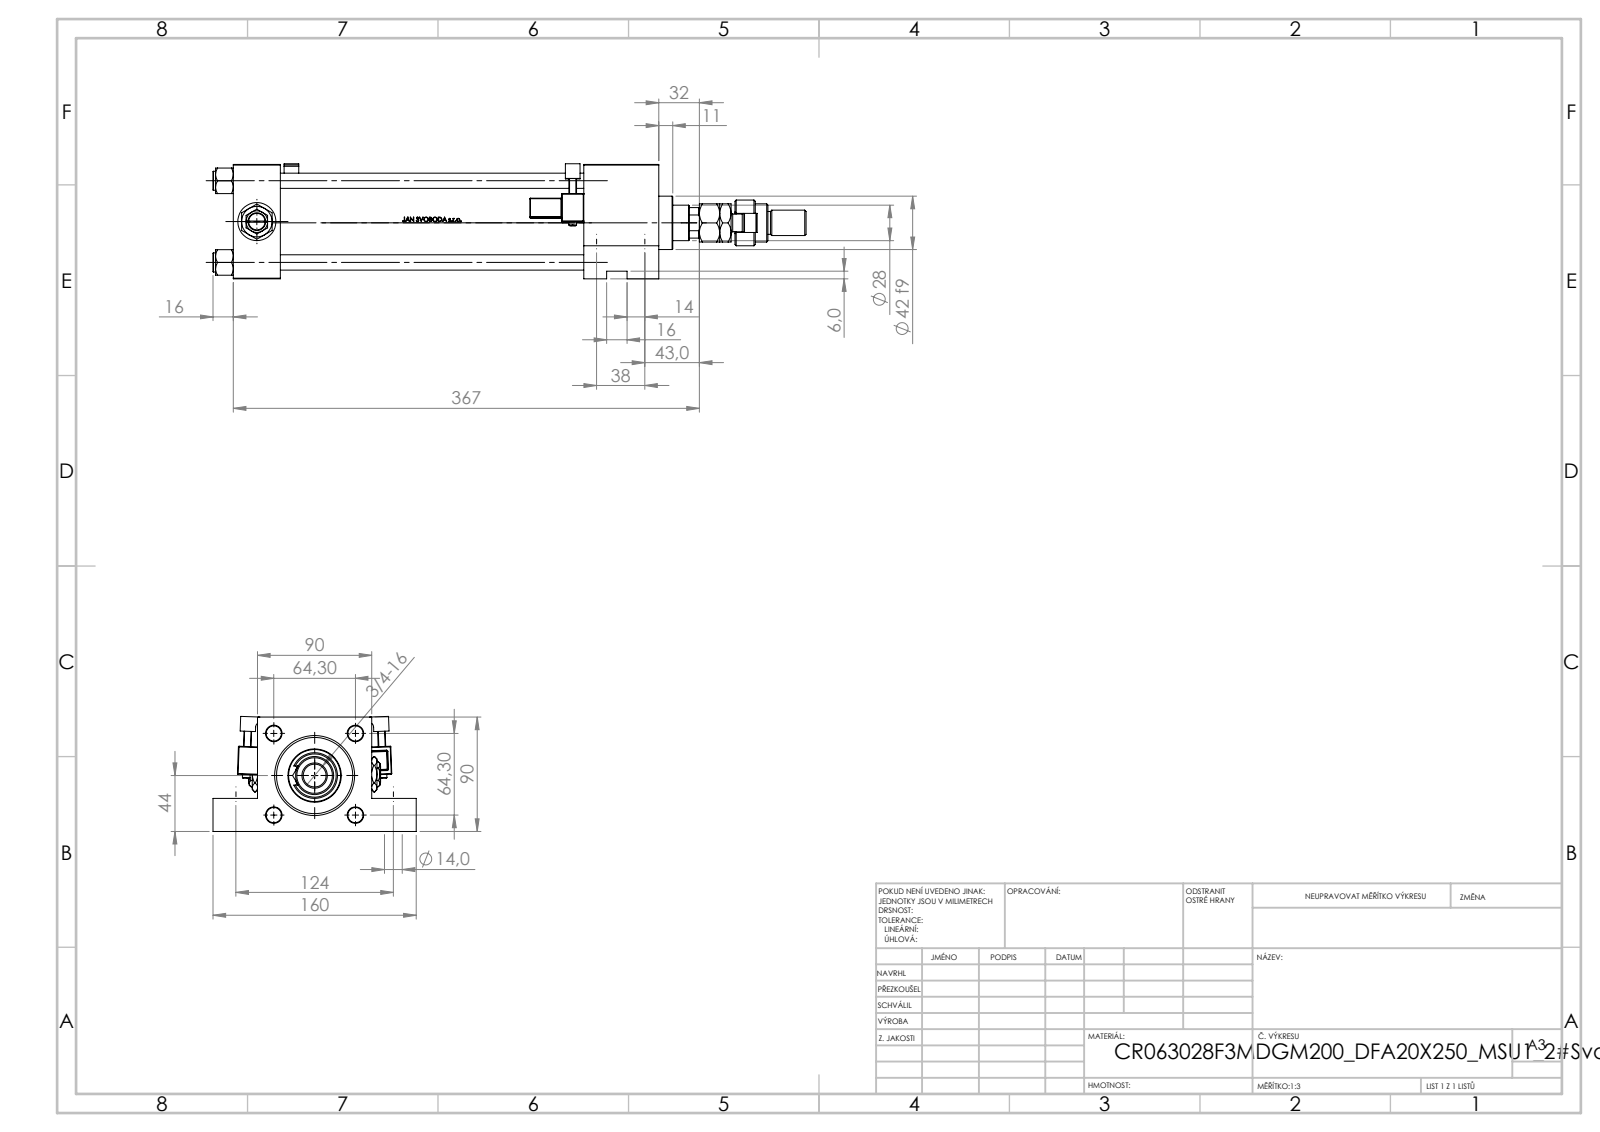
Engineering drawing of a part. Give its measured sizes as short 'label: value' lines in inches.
name: V215CR_VCP_F; V215_VC_A; MFA; Zatka_pro_OIL_PORT (+5 more)
written by: SolidWorks 2019 (CONFIG_CONTROL_DESIGN)
unit: in
bodies: 17 solids, 1432 faces (569 planar, 203 cylindrical, 660 other)
size: 18.386 × 6.299 × 3.564
volume: 86.71 in³; area: 528.3 in²
holes: 4× ⌀0.472, 4× ⌀0.551, 3× ⌀0.825, 3× ⌀1.181, 2× ⌀0.276, 1× ⌀0.728, 1× ⌀1.102, 1× ⌀1.22, 1× ⌀1.969, 1× ⌀2.362, 1× ⌀2.48
bosses: 4× ⌀0.591, 2× ⌀0.236, 1× ⌀2.717, 1× ⌀1.654, 1× ⌀1.417, 1× ⌀1.181, 1× ⌀0.866, 1× ⌀0.787
rounds: 48× R0.02, 2× R0.039, 2× R0.098, 2× R0.157, 1× R0.295, 1× R0.472, 1× R0.531
face distances: 3.543, 1.457, 13.189, 11.732, 2.323, 10.866, 9.409, 1.024, 2.52, 1.378
hole spacings: 2.531, 1.496, 1.763, 1.818, 2.472, 2.678, 3.58, 4.882
